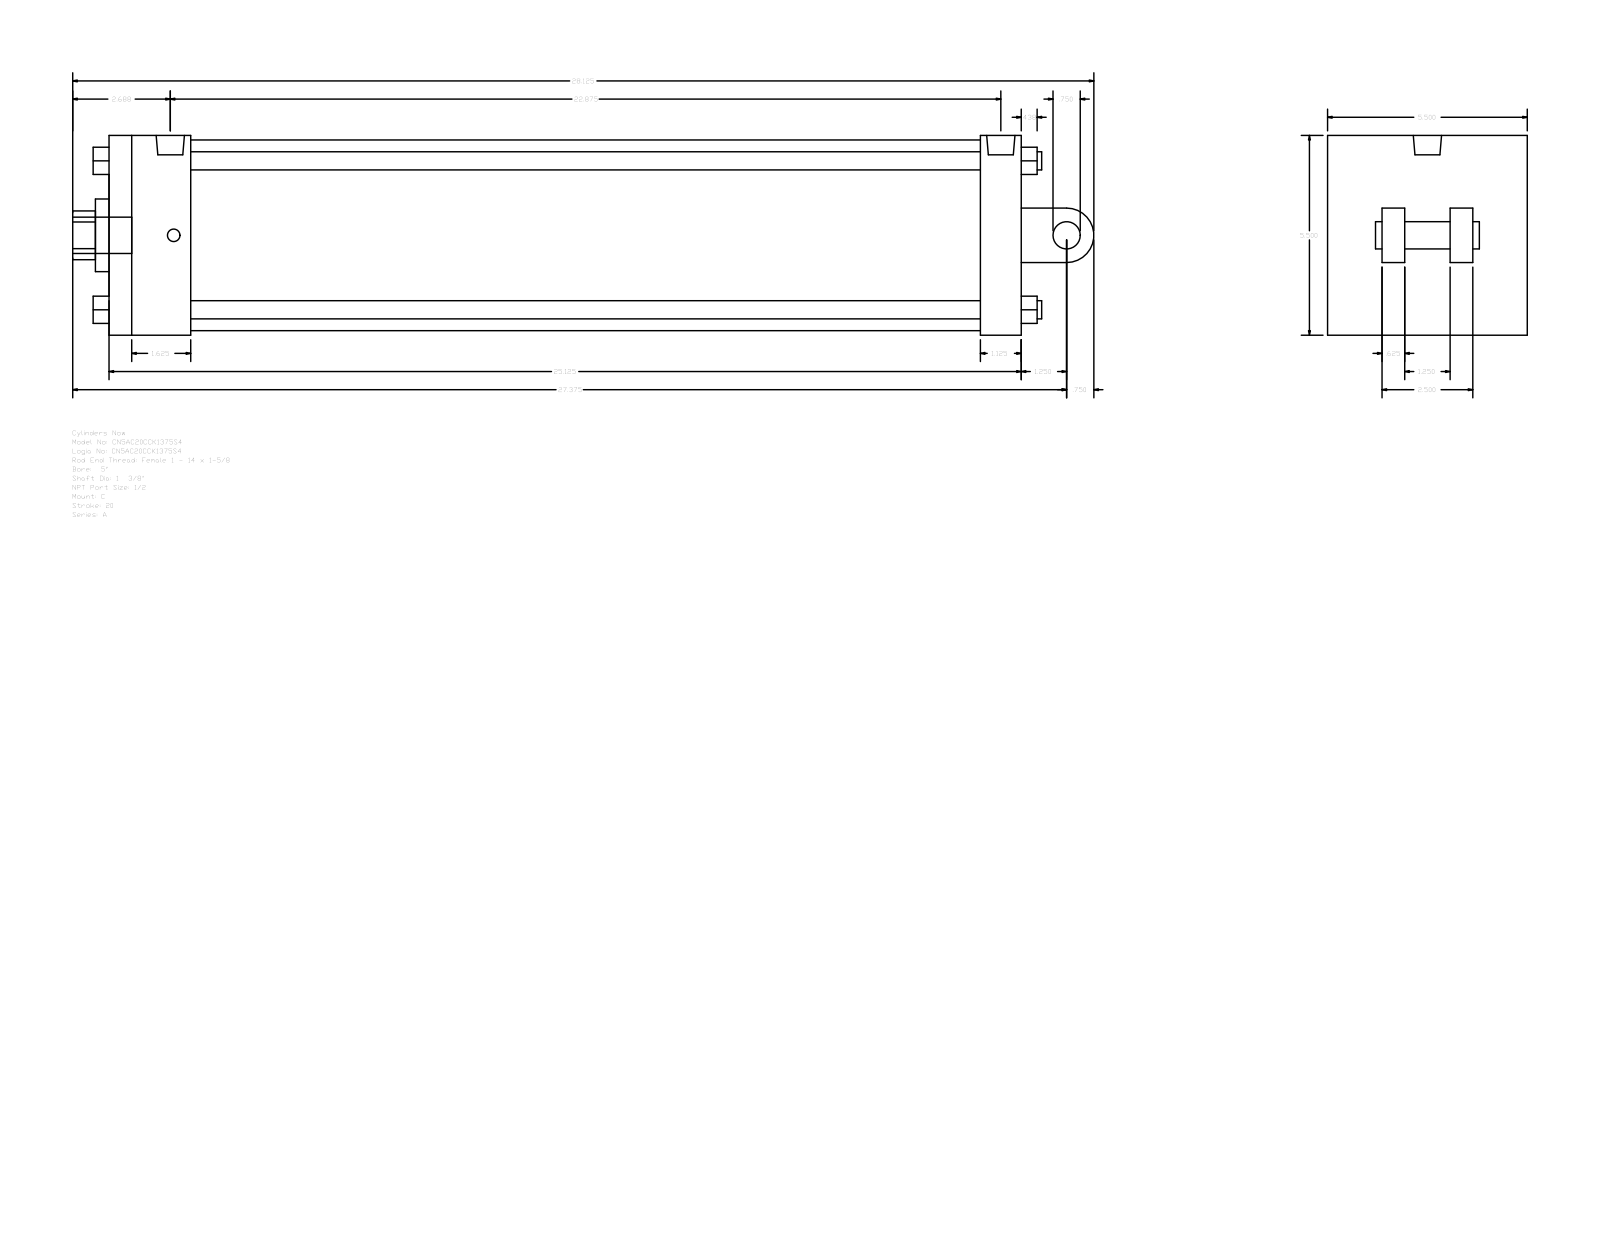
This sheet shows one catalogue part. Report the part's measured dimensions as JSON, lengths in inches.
{"part_name": "A_C__0500_1.375", "step_written_by": "GSSL Pune (CONFIG_CONTROL_DESIGN)", "units": "inches", "bodies": {"solids": 0, "faces": 135, "planar": 102, "cylindrical": 33, "other": 0}, "overall_size": [28.125, 5.5, 5.5], "round_holes": [[0.344, 2], [0.778, 1], [1.375, 1], [2, 1], [5.25, 1]], "round_bosses_or_shafts": [[0.5, 4], [0.344, 2], [1, 1], [0.778, 1], [0.75, 1]], "partial_cylinders_radius": [[0.672, 1], [0.75, 1]], "face_to_face_distances": [5.5, 25.125, 1.125, 2.25, 24, 21.75, 22.875, 1.5, 0.625, 2.125], "hole_center_spacings": [0.094]}
